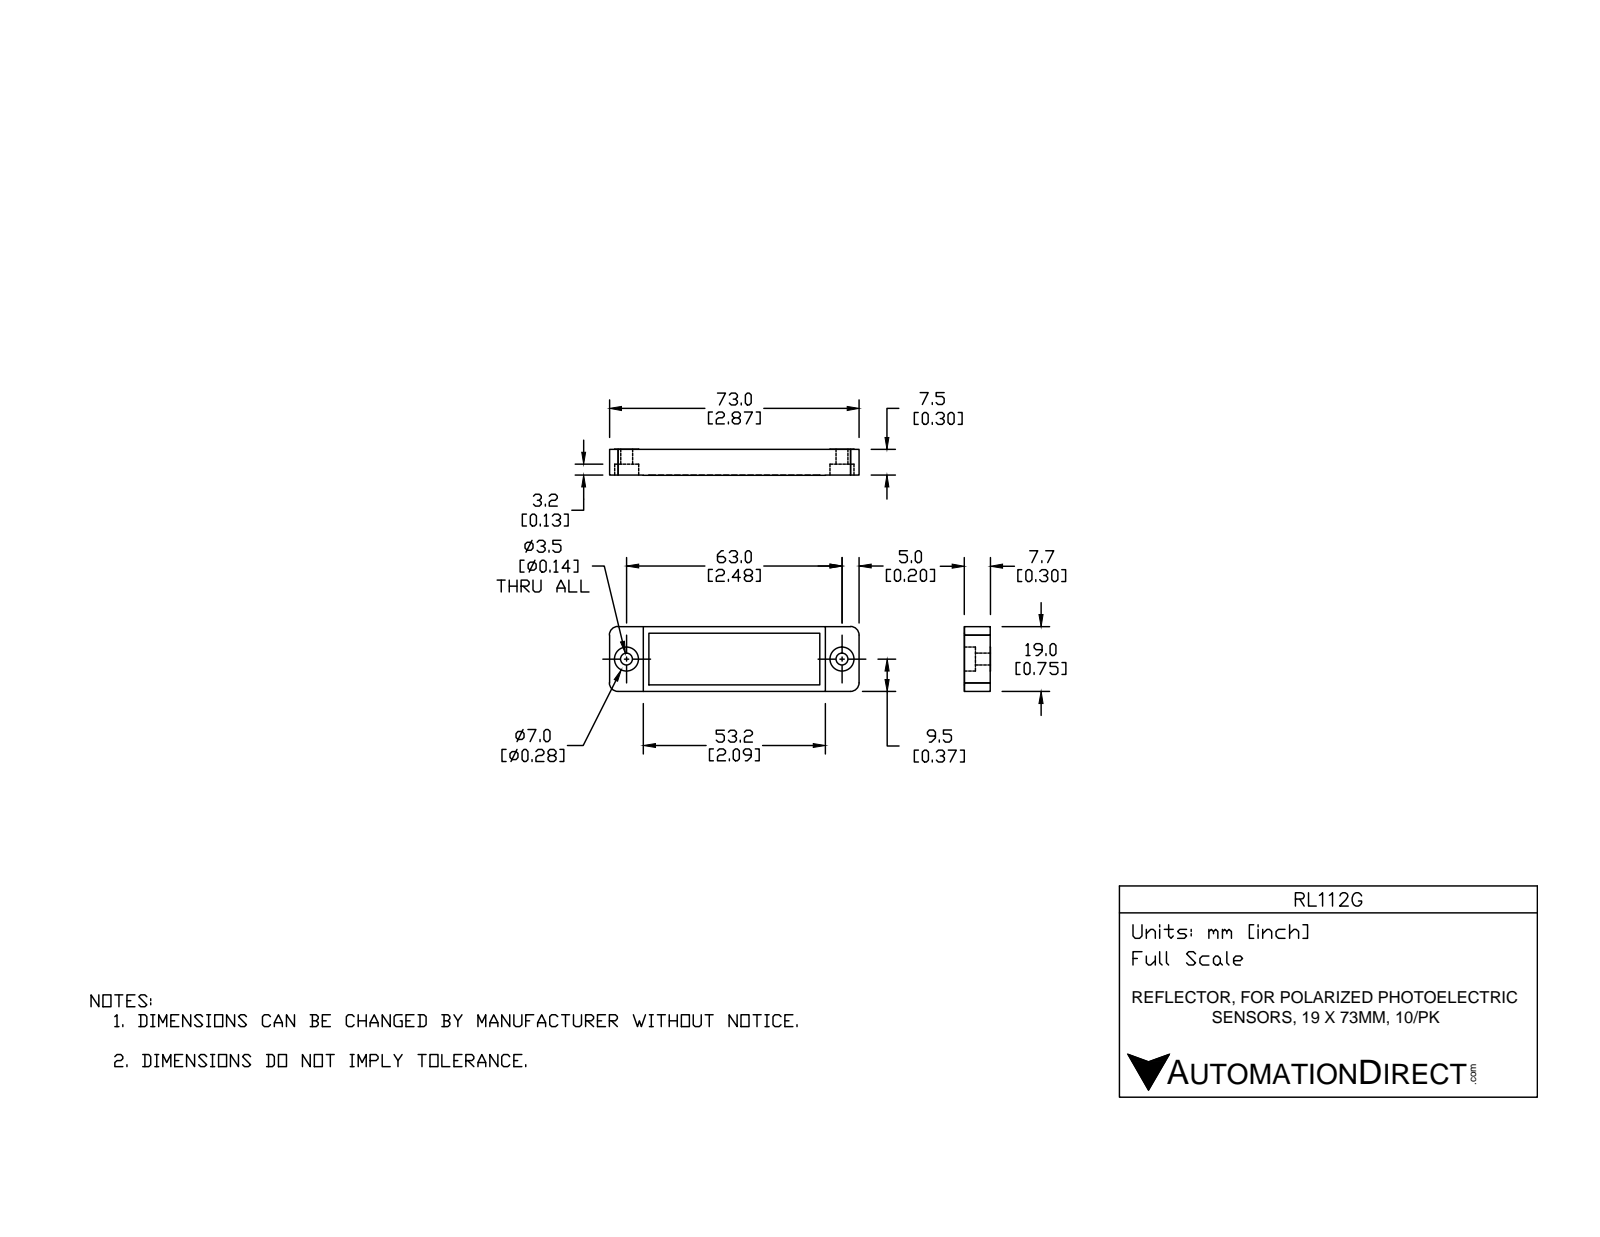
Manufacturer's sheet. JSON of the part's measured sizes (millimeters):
{"part_name": "RL-112G", "step_written_by": "SolidWorks 2017 (AUTOMOTIVE_DESIGN)", "units": "millimeters", "bodies": {"solids": 1, "faces": 35, "planar": 19, "cylindrical": 16, "other": 0}, "overall_size": [73, 19, 7.7], "volume_mm3": 10100, "surface_area_mm2": 4342, "round_holes": [[3.5, 2], [7, 2]], "partial_cylinders_radius": [[2.5, 4]], "face_to_face_distances": [7.5, 19, 7.6, 73, 4.3, 3.2, 3.3, 4.4, 7.7, 2], "hole_center_spacings": [63]}
